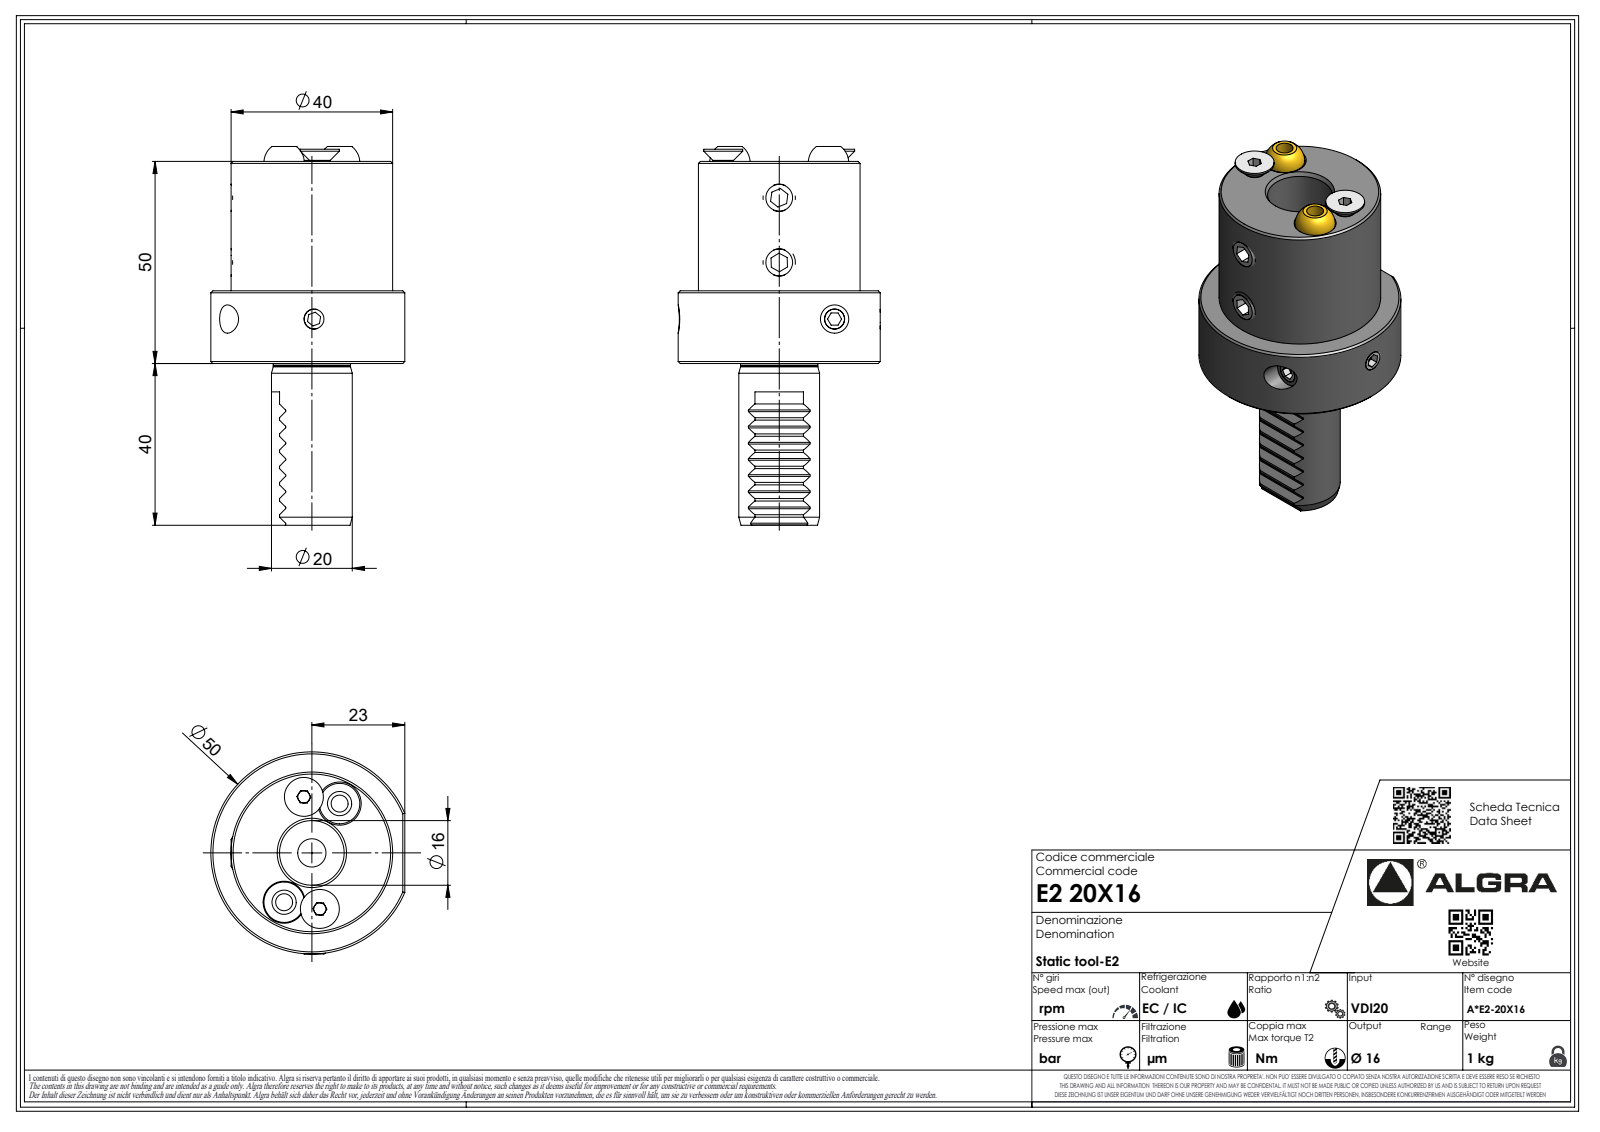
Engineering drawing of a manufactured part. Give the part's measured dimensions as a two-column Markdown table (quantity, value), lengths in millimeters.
| quantity | value |
| --- | --- |
| part name | E220X16 |
| STEP written by | SolidWorks 2023 (AUTOMOTIVE_DESIGN) |
| units | millimeters |
| bodies | 1 solid, 261 faces (177 planar, 39 cylindrical, 45 other) |
| overall size | 93.7 × 50 × 48 |
| volume | 86 574 mm³ |
| surface area | 14 267 mm² |
| round holes (diameter × count) | 1.05 × 1, 16 × 1 |
| round bosses / shafts (diameter × count) | 50 × 1, 40 × 1, 20 × 1, 19.1 × 1, 3.18 × 1, 0.85 × 1 |
| partial cylindrical surfaces (radius × count) | 0.3 × 8, 0.17 × 7, 0.26 × 7, 1.85 × 7, 0.1 × 1 |
| main face-to-face distances | 50, 18, 32, 2.83, 40, 58, 90, 88, 48, 30 |
